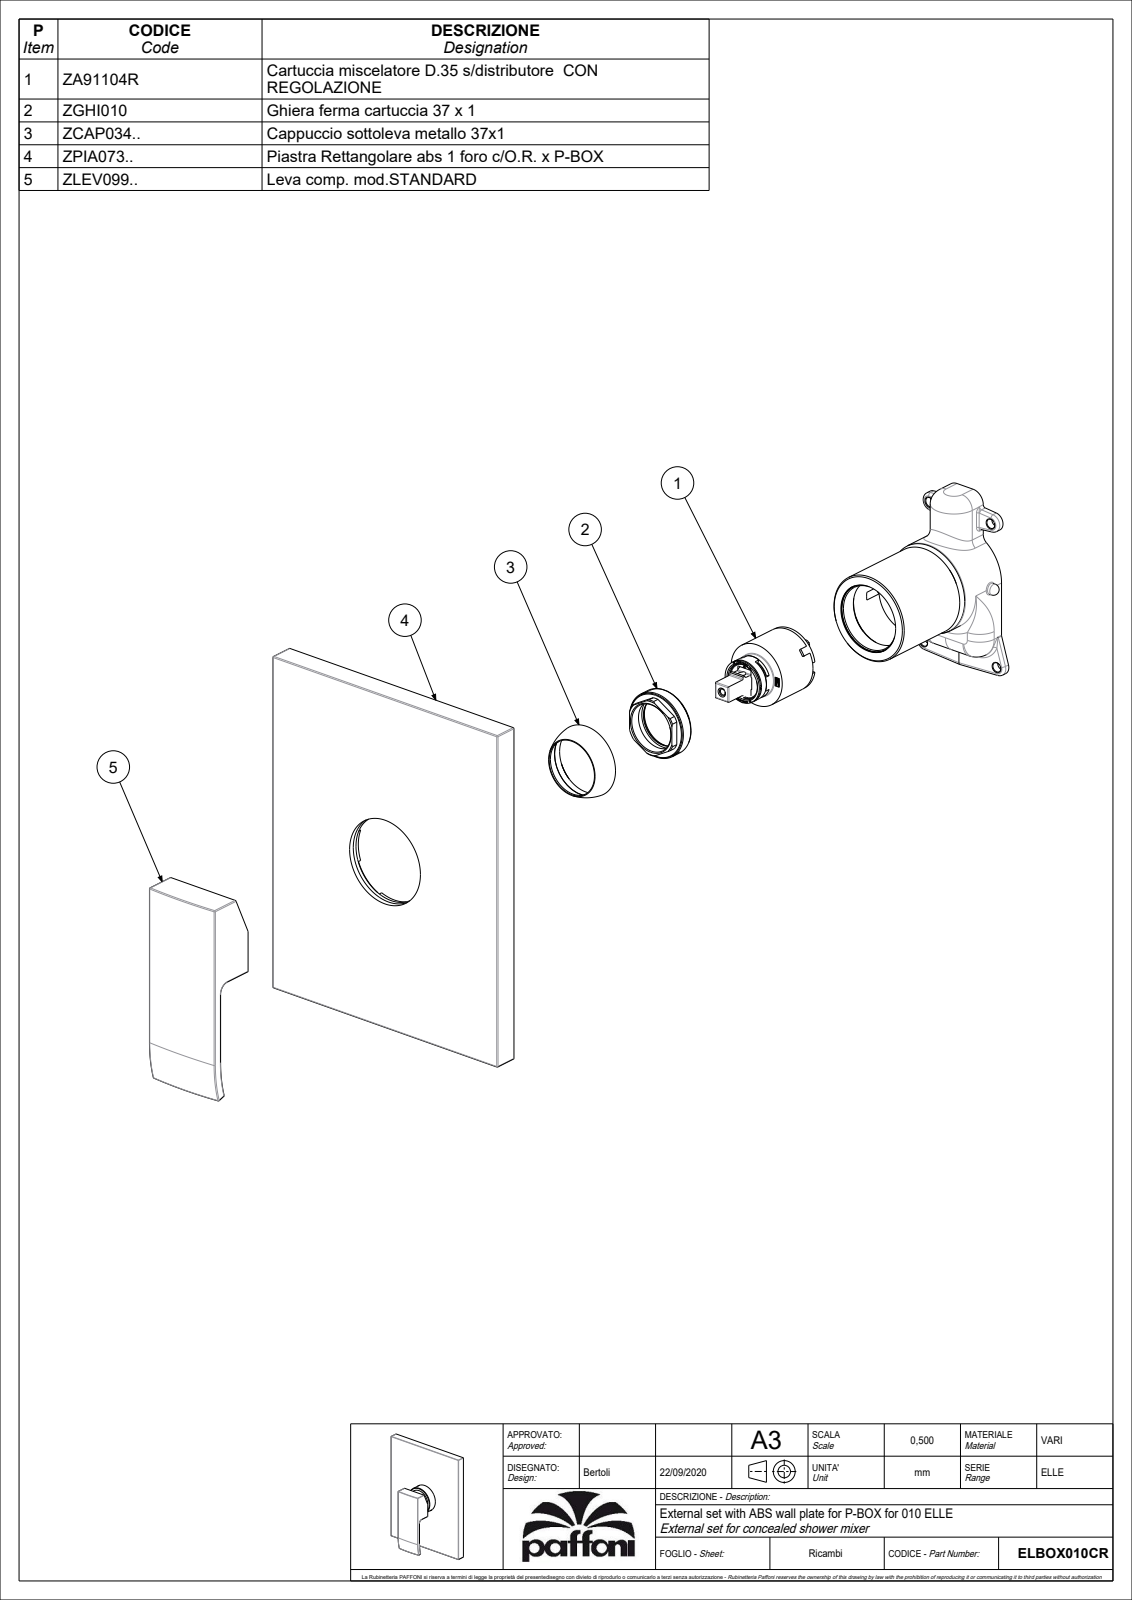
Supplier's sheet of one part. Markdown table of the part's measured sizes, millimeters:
| quantity | value |
| --- | --- |
| part name | LESBOX010CR |
| STEP written by | CREO PARAMETRIC BY PTC INC, 2020044 (CONFIG_CONTROL_DESIGN) |
| units | millimeters |
| bodies | 1 solid, 144 faces (42 planar, 58 cylindrical, 44 other) |
| overall size | 192 × 154 × 65.1 |
| volume | 483 458 mm³ |
| surface area | 91 101 mm² |
| round holes (diameter × count) | 3 × 1, 5.5 × 1, 7.8 × 1 |
| round bosses / shafts (diameter × count) | 48.1 × 1, 7.6 × 1, 5 × 1 |
| partial cylindrical surfaces (radius × count) | 0.5 × 18, 1.5 × 14, 2 × 4, 300 × 2 |
| main face-to-face distances | 13.5, 54.5, 99.5, 154, 45, 192, 73.5, 118.5, 62.3, 48.8 |
